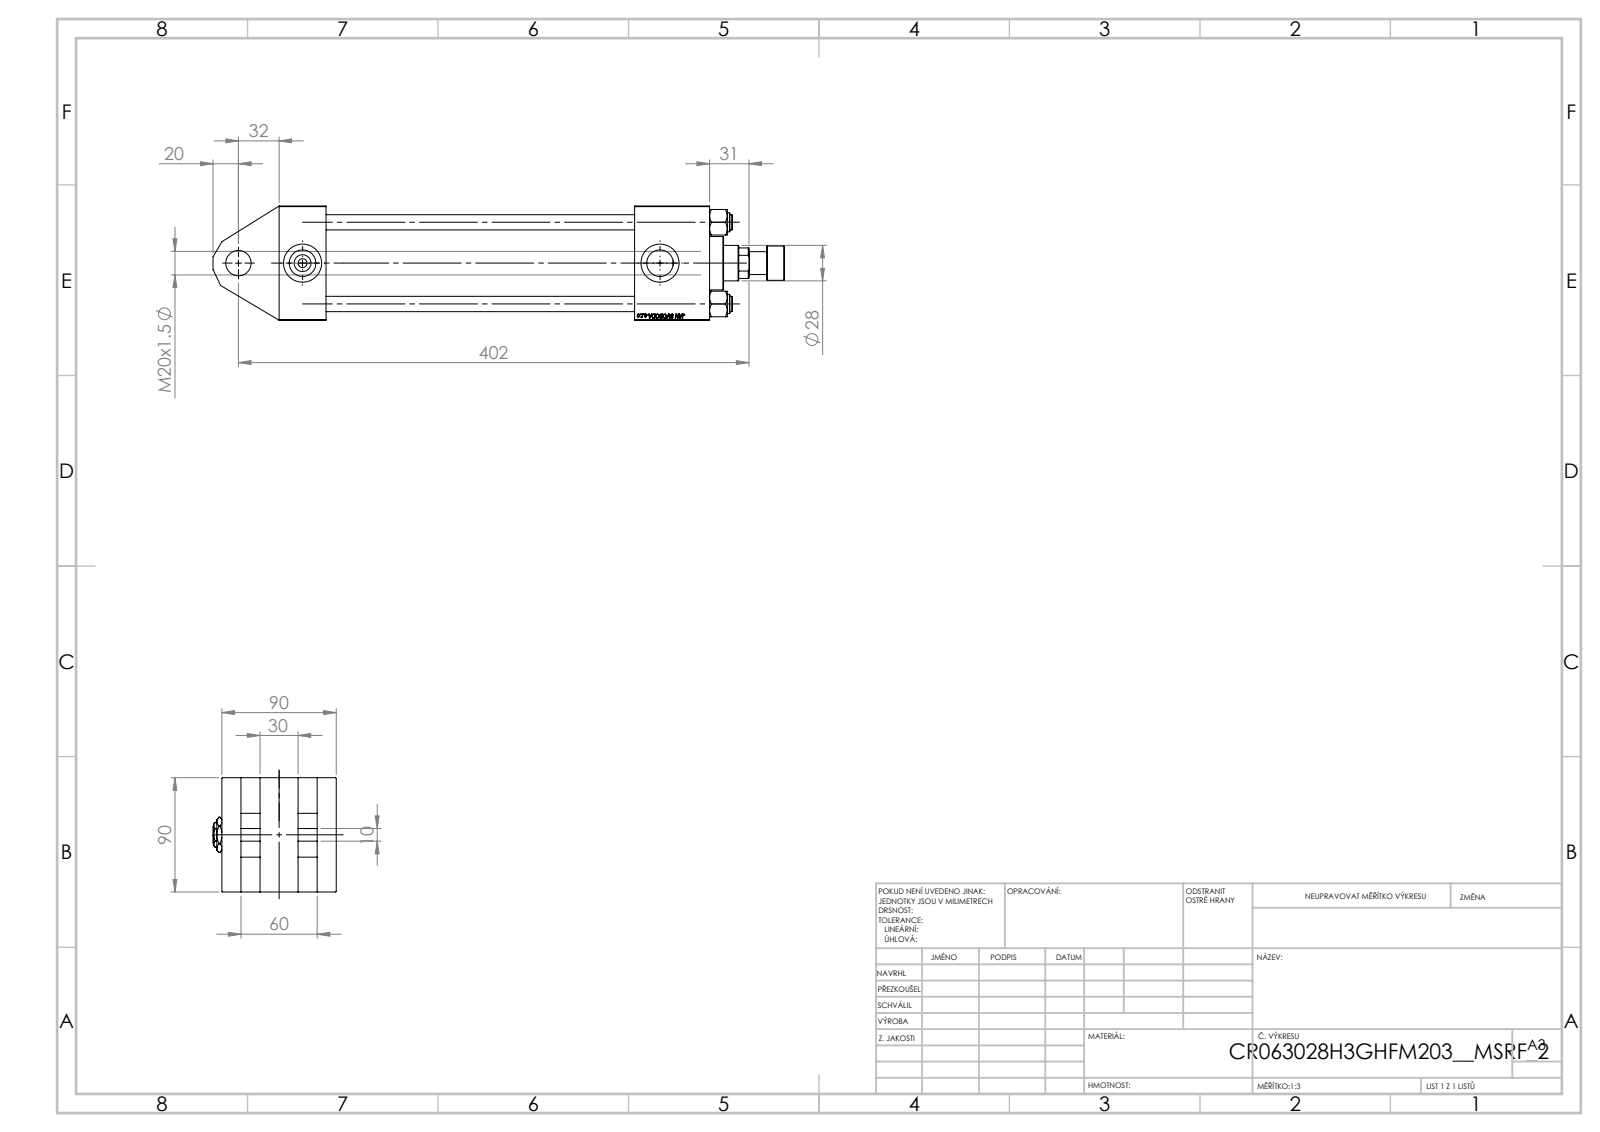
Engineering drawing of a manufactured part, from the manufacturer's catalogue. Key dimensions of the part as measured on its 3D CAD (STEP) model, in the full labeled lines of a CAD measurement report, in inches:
Part name (STEP PRODUCT): V215_VC_A; Zatka_pro_OIL_PORT; V215CR_ROD_END_F; V215CR_H_Body (+3 more)
STEP written by: SolidWorks 2019 (CONFIG_CONTROL_DESIGN)
Units: inches
Bodies: 14 solids, 1244 faces (570 planar, 98 cylindrical, 576 other)
Overall size (bounding box): 17.717 × 3.819 × 3.543
Volume: 82.63 in³ · Surface area: 503.4 in²
Round holes (diameter × count): ⌀0.472 ×4, ⌀0.276 ×2, ⌀0.825 ×2, ⌀1.181 ×2, ⌀0.728 ×1, ⌀0.787 ×1, ⌀1.102 ×1, ⌀1.22 ×1, ⌀1.969 ×1, ⌀2.362 ×1, ⌀2.48 ×1
Round bosses / shafts (diameter × count): ⌀0.591 ×4, ⌀2.717 ×1, ⌀1.654 ×1, ⌀1.063 ×1, ⌀0.709 ×1
Main face-to-face distances: 3.543, 0.591, 2.362, 1.181, 11.89, 1.772, 1.457, 2.323, 2.953, 13.346
Hole centre spacings: 1.79, 2.531, 3.58, 1.988, 11.083, 13.071
